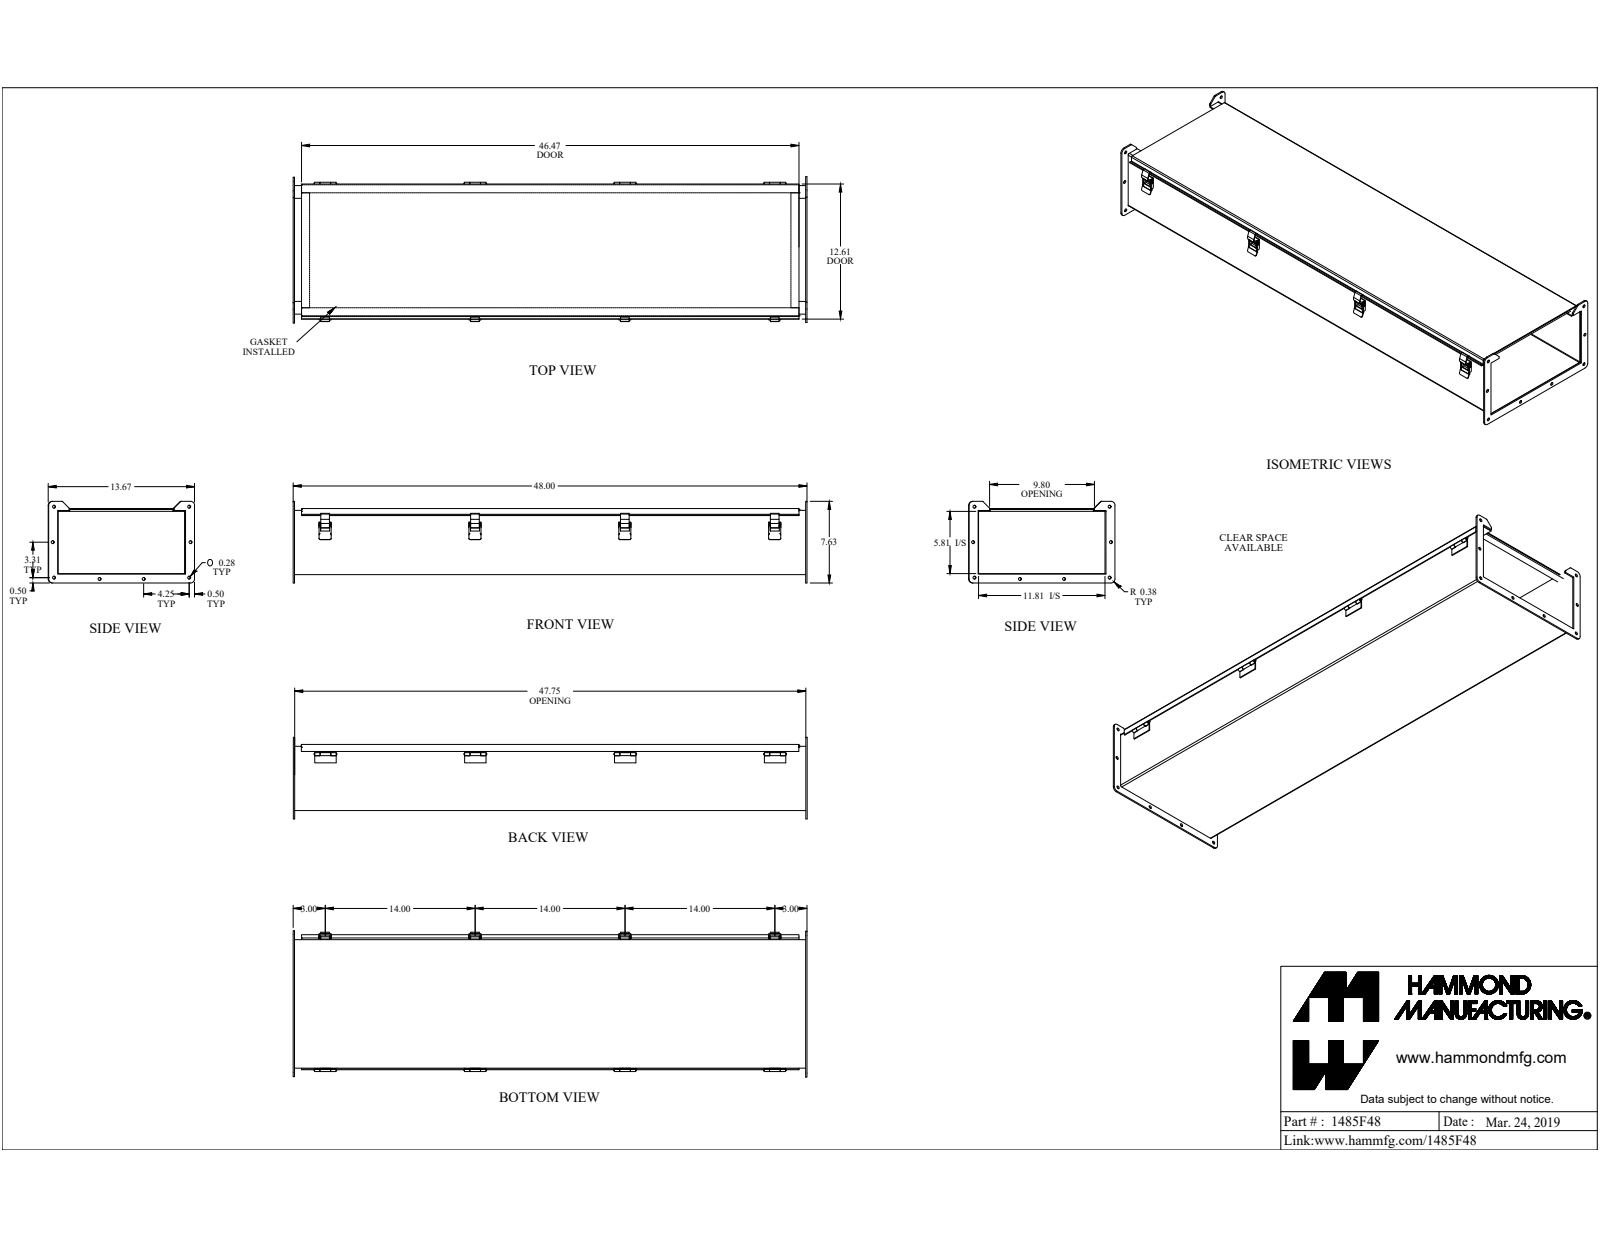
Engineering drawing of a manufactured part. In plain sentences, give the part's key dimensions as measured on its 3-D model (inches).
The part is named "1485F48". Its 3-D file was written by "SolidWorks 2019 (CONFIG_CONTROL_DESIGN)". It is 32 solids with 708 faces: 418 planar, 282 cylindrical and 8 other. Overall it measures 48 by 13.67 by 7.625 inches. Its volume is 187.2 cubic inches and its surface area 4 168 square inches. Round holes: 16 of diameter 0.281, 1 of diameter 0.125, 1 of diameter 0.13, 1 of diameter 0.164. Round bosses or shafts: 2 of diameter 0.187, 1 of diameter 0.275, 1 of diameter 0.156, 1 of diameter 0.125, 1 of diameter 0.125. Partial cylindrical surfaces (rounded edges, fillets, slot ends): 25 of radius 0.016, 17 of radius 0.125, 9 of radius 0.035, 9 of radius 0.039, 9 of radius 0.076, 8 of radius 0.015, 8 of radius 0.029, 8 of radius 0.086. The main face-to-face distances are 0.095, 0.072, 6.1, 6.172, 6.005, 6.077, 11.905, 12, 11.81, 5.905. The hole center spacings are 0.045, 3.315, 6.625, 13.173, 3.313, 3.317, 4.252, 5.564.
